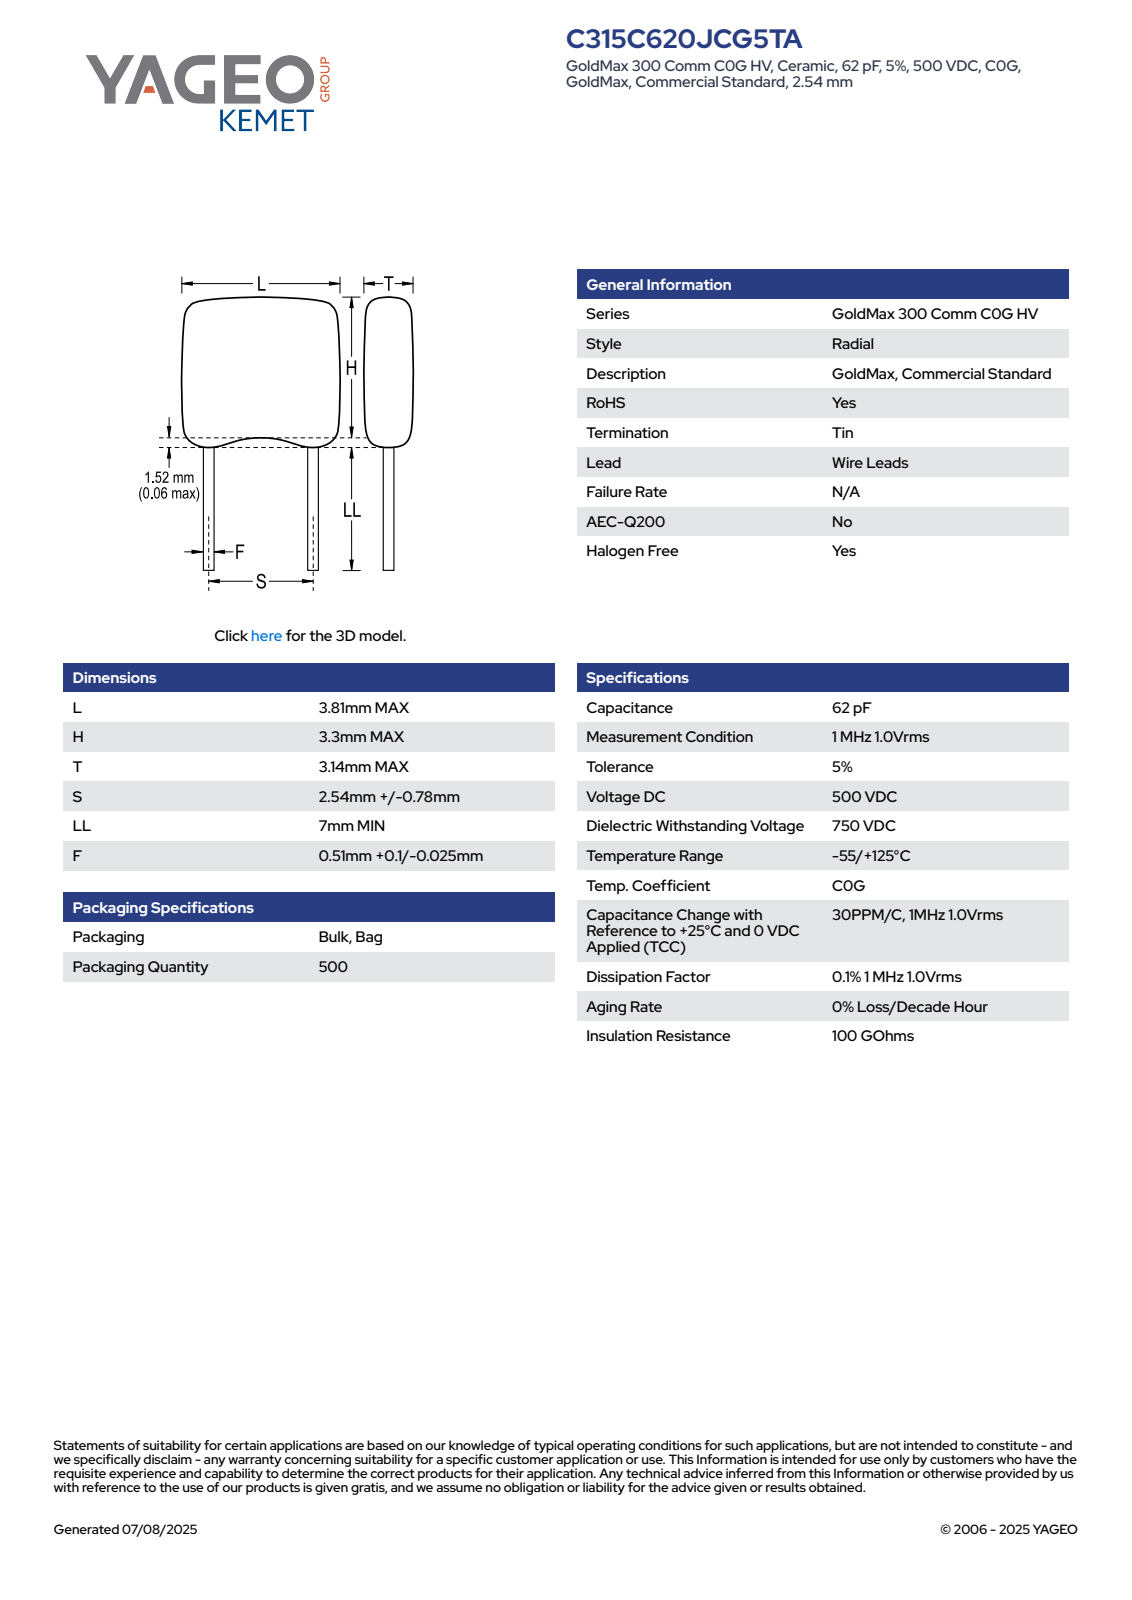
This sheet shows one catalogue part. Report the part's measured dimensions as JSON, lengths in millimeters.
{"part_name": "CCR_KRCST_C315_L3.81H3.3T3.14S2.54LL7F0.61", "step_written_by": "SolidWorks 2014 (AUTOMOTIVE_DESIGN)", "units": "millimeters", "bodies": {"solids": 4, "faces": 83, "planar": 65, "cylindrical": 14, "other": 4}, "overall_size": [11.82, 3.81, 3.15], "volume_mm3": 57, "surface_area_mm2": 105, "round_bosses_or_shafts": [[0.61, 2]], "partial_cylinders_radius": [[0.75, 10]], "face_to_face_distances": [3.14, 3.81, 4.82, 7, 11.82, 0.41, 9.66, 2.66, 2.16, 9.25]}
